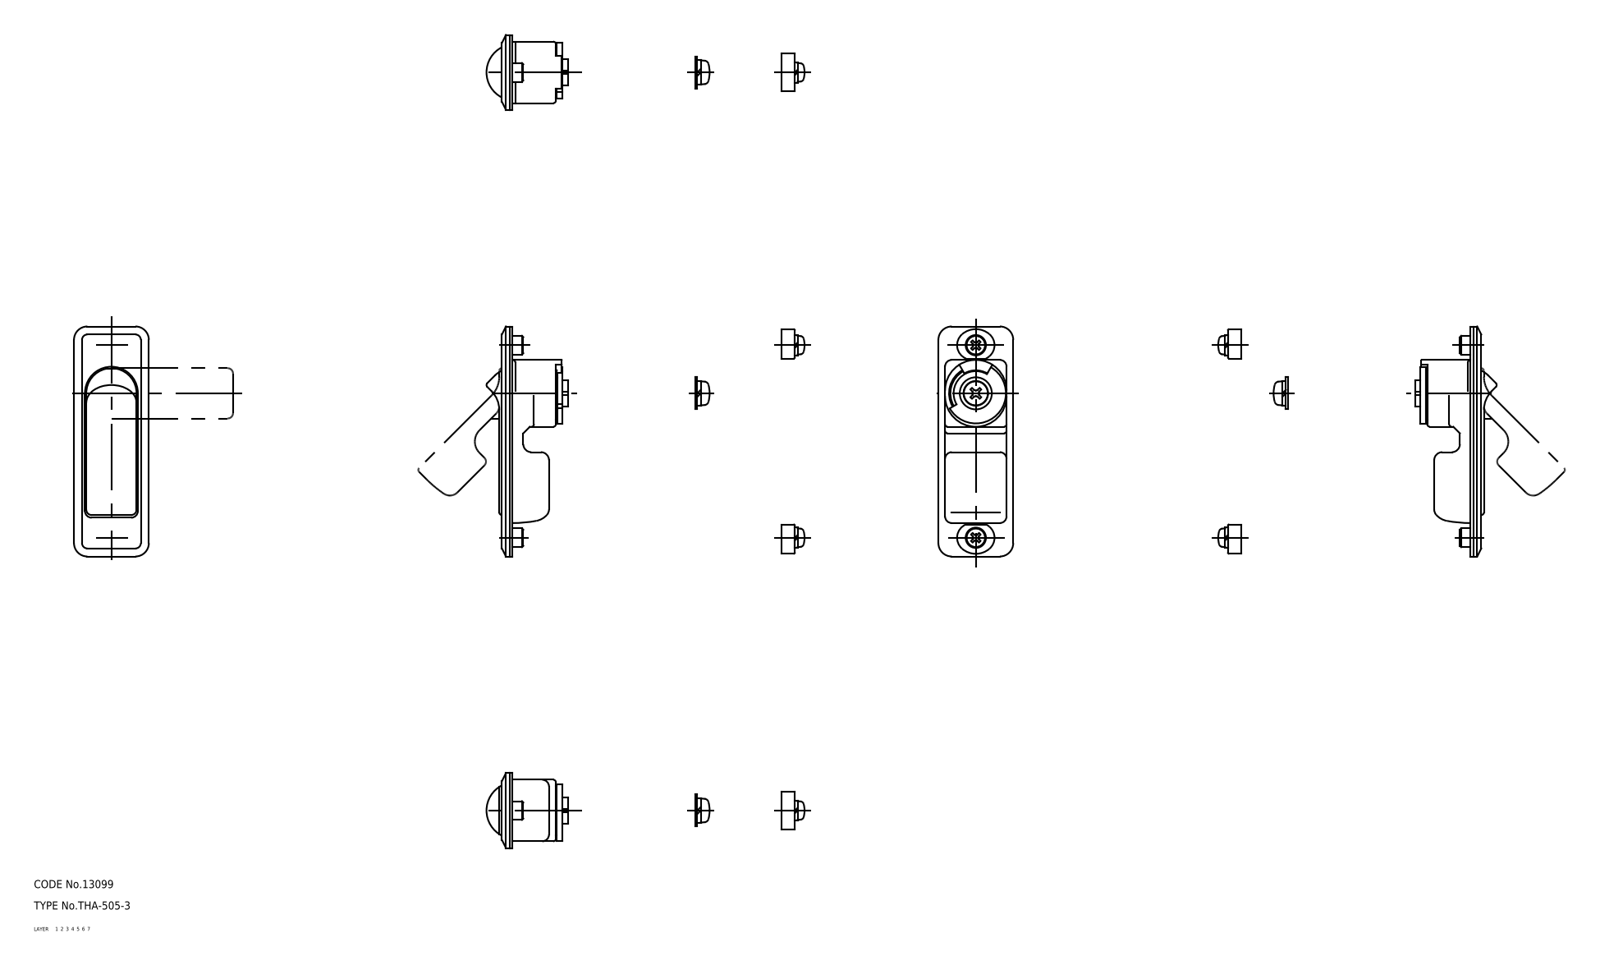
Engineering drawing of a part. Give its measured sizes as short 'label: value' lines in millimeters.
name: screw_B; bracket; shaft; screw_A (+6 more)
written by: CADfix (AUTOMOTIVE_DESIGN)
unit: mm
bodies: 11 solids, 391 faces (0 planar, 0 cylindrical, 391 other)
size: 86 × 35.83 × 28
volume: 25 200 mm³; area: 20 250 mm²
